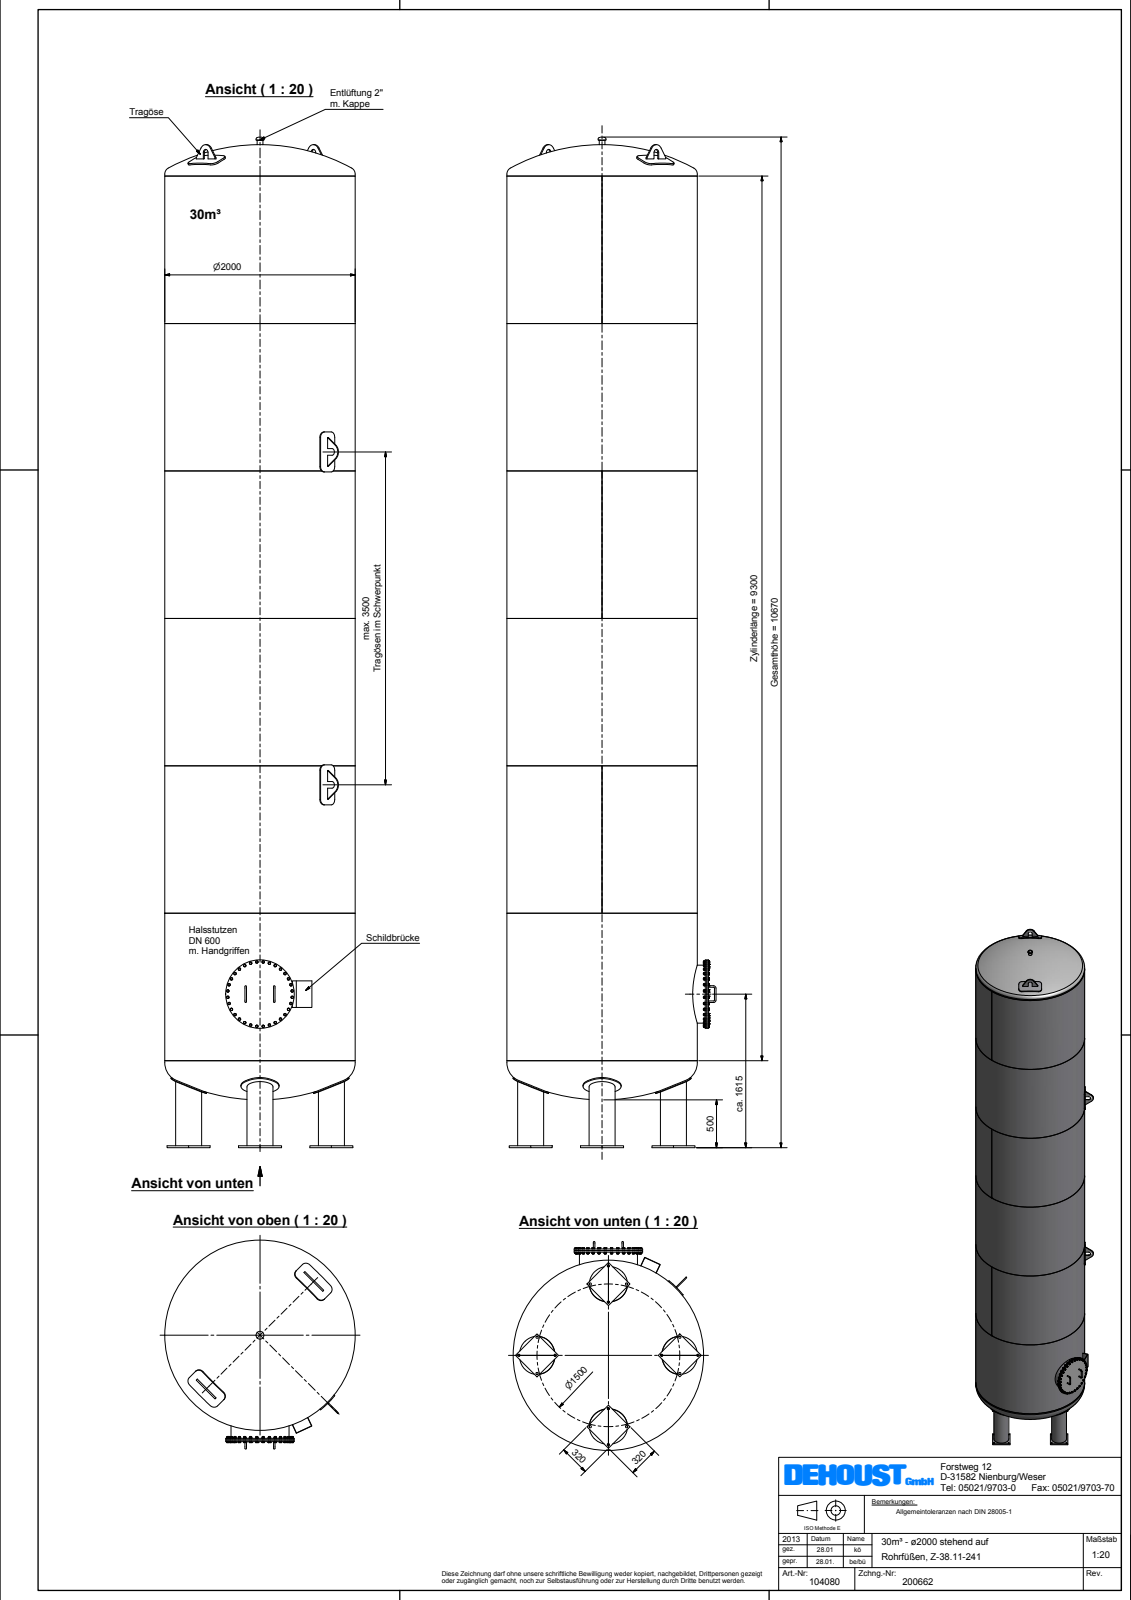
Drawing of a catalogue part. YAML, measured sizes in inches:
part_name: "Beh\\S\\dlter_Z-38_11-241_2000_030_KV"
step_written_by: "Autodesk Inventor 2012 (AUTOMOTIVE_DESIGN)"
units: inches
bodies: {solids: 7, faces: 1128, planar: 640, cylindrical: 166, other: 322}
overall_size: [418.324, 86.496, 78.74]
volume: 78780
surface_area: 216200
round_holes:
  - {diameter: 10.118, count: 4}
  - {diameter: 23.543, count: 1}
  - {diameter: 78.268, count: 1}
round_bosses_or_shafts:
  - {diameter: 0.63, count: 38}
  - {diameter: 0.886, count: 32}
  - {diameter: 15.748, count: 4}
  - {diameter: 10.748, count: 4}
  - {diameter: 78.74, count: 1}
  - {diameter: 28.346, count: 1}
  - {diameter: 25.984, count: 1}
  - {diameter: 24.016, count: 1}
partial_cylinders:
  - {radius: 2.205, count: 16}
  - {radius: 1.378, count: 4}
  - {radius: 3.346, count: 4}
  - {radius: 39.764, count: 1}
face_to_face_distances: [36.007, 0.787, 1.378, 35.22, 0.63, 0.748, 0.394, 0.118, 0.116, 6.968]
hole_center_spacings: [29.528, 41.758, 59.055]
